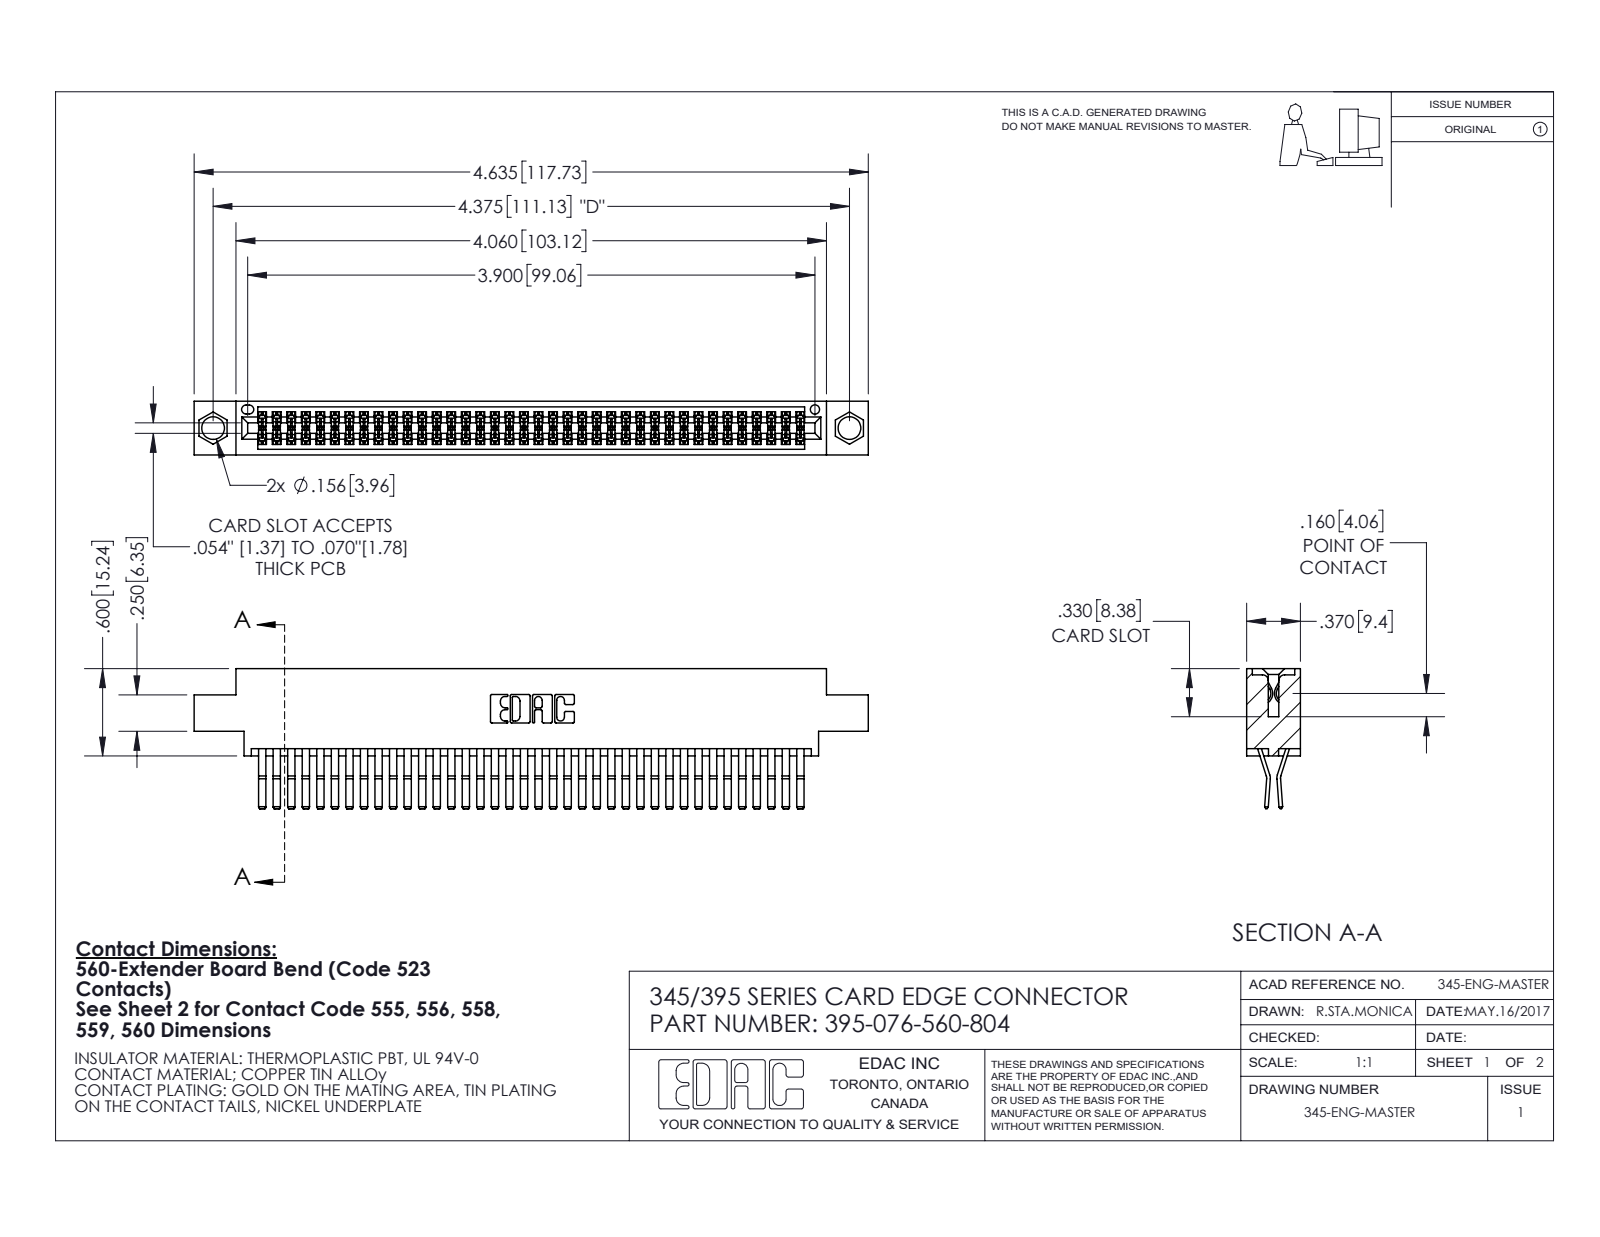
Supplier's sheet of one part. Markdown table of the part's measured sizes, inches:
| quantity | value |
| --- | --- |
| part name | 345-292-001_560 Tail; 395-076-560-804; 345 Part_0.170 Offset - 0.156 Dia-TI |
| STEP written by | SolidWorks 2020 (CONFIG_CONTROL_DESIGN) |
| units | inches |
| bodies | 77 solids, 4096 faces (2606 planar, 1490 cylindrical, 0 other) |
| overall size | 4.635 × 0.962 × 0.37 |
| volume | 0.713 in³ |
| surface area | 28.61 in² |
| round holes (diameter × count) | 0.156 × 2, 0.064 × 1 |
| partial cylindrical surfaces (radius × count) | 0.006 × 152, 0.01 × 22, 0.007 × 6, 0.031 × 6, 0.026 × 3, 0.01 × 2, 0.014 × 2, 0.019 × 2 |
| main face-to-face distances | 0.025, 0.072, 0.298, 0.37, 0.2, 0.098, 0.272, 0.225, 0.175, 0.149 |
| hole center spacings | 0.27, 4.139, 4.375 |
